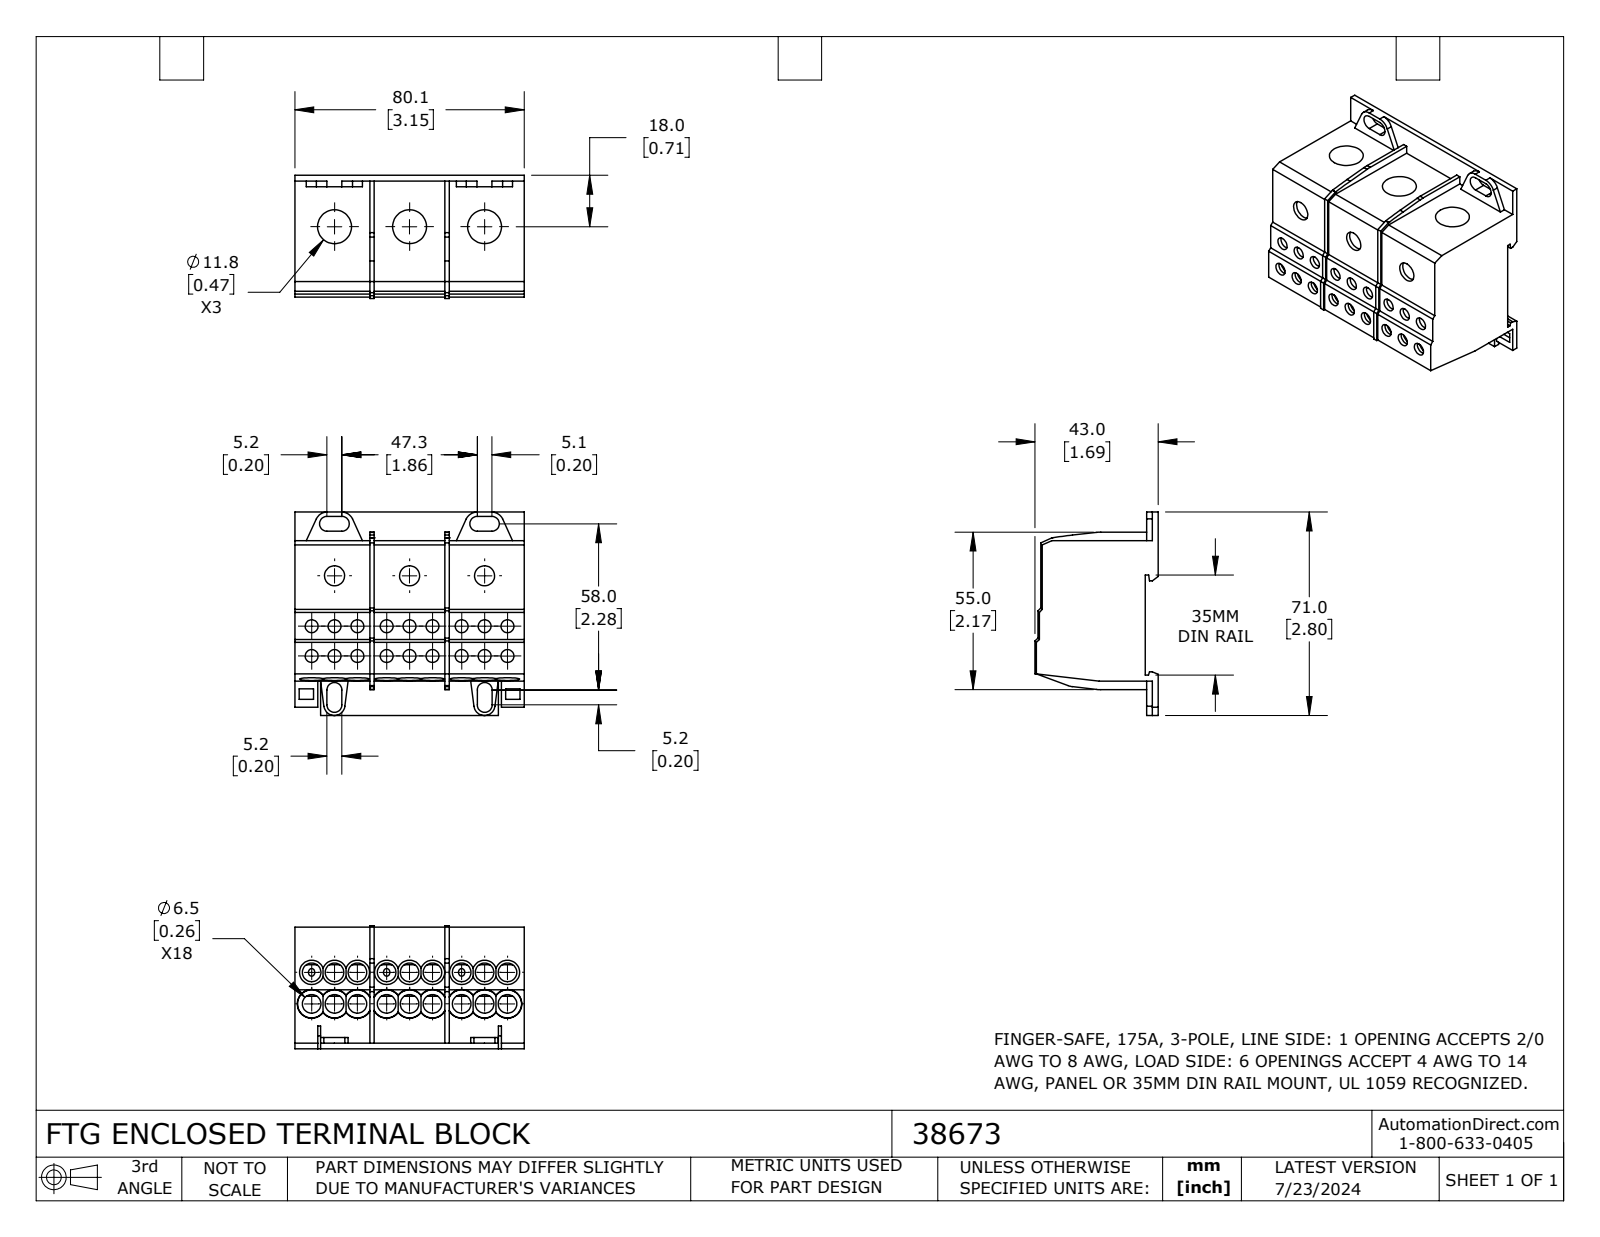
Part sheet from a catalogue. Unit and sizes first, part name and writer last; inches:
Units: inches
Overall size (bounding box): 3.154 × 2.795 × 1.693
Round holes (diameter × count): ⌀0.256 ×27, ⌀0.177 ×18, ⌀0.264 ×9, ⌀0.335 ×6, ⌀0.276 ×3, ⌀0.413 ×3, ⌀0.466 ×3, ⌀0.394 ×2
Partial cylindrical surfaces — rounded edges, fillets, slot ends (radius × count): R0.098 ×18, R0.187 ×13, R0.102 ×9, R0.197 ×7, R0.161 ×4, R0.167 ×3, R0.146 ×2, R0.533 ×2
Main face-to-face distances: 0.177, 0.079, 1.594, 0.059, 0.098, 3.154, 1.417, 0.039, 1.457, 1.516
Hole centre spacings: 1.031, 0.315, 0.717, 1.346, 2.063, 0.517, 0.535, 0.63
Volume: 7.439 in³ · Surface area: 58.02 in²
Bodies: 1 solid, 651 faces (267 planar, 286 cylindrical, 98 other)
Part name (STEP PRODUCT): 38673
STEP written by: SolidWorks 2023 (CONFIG_CONTROL_DESIGN)
